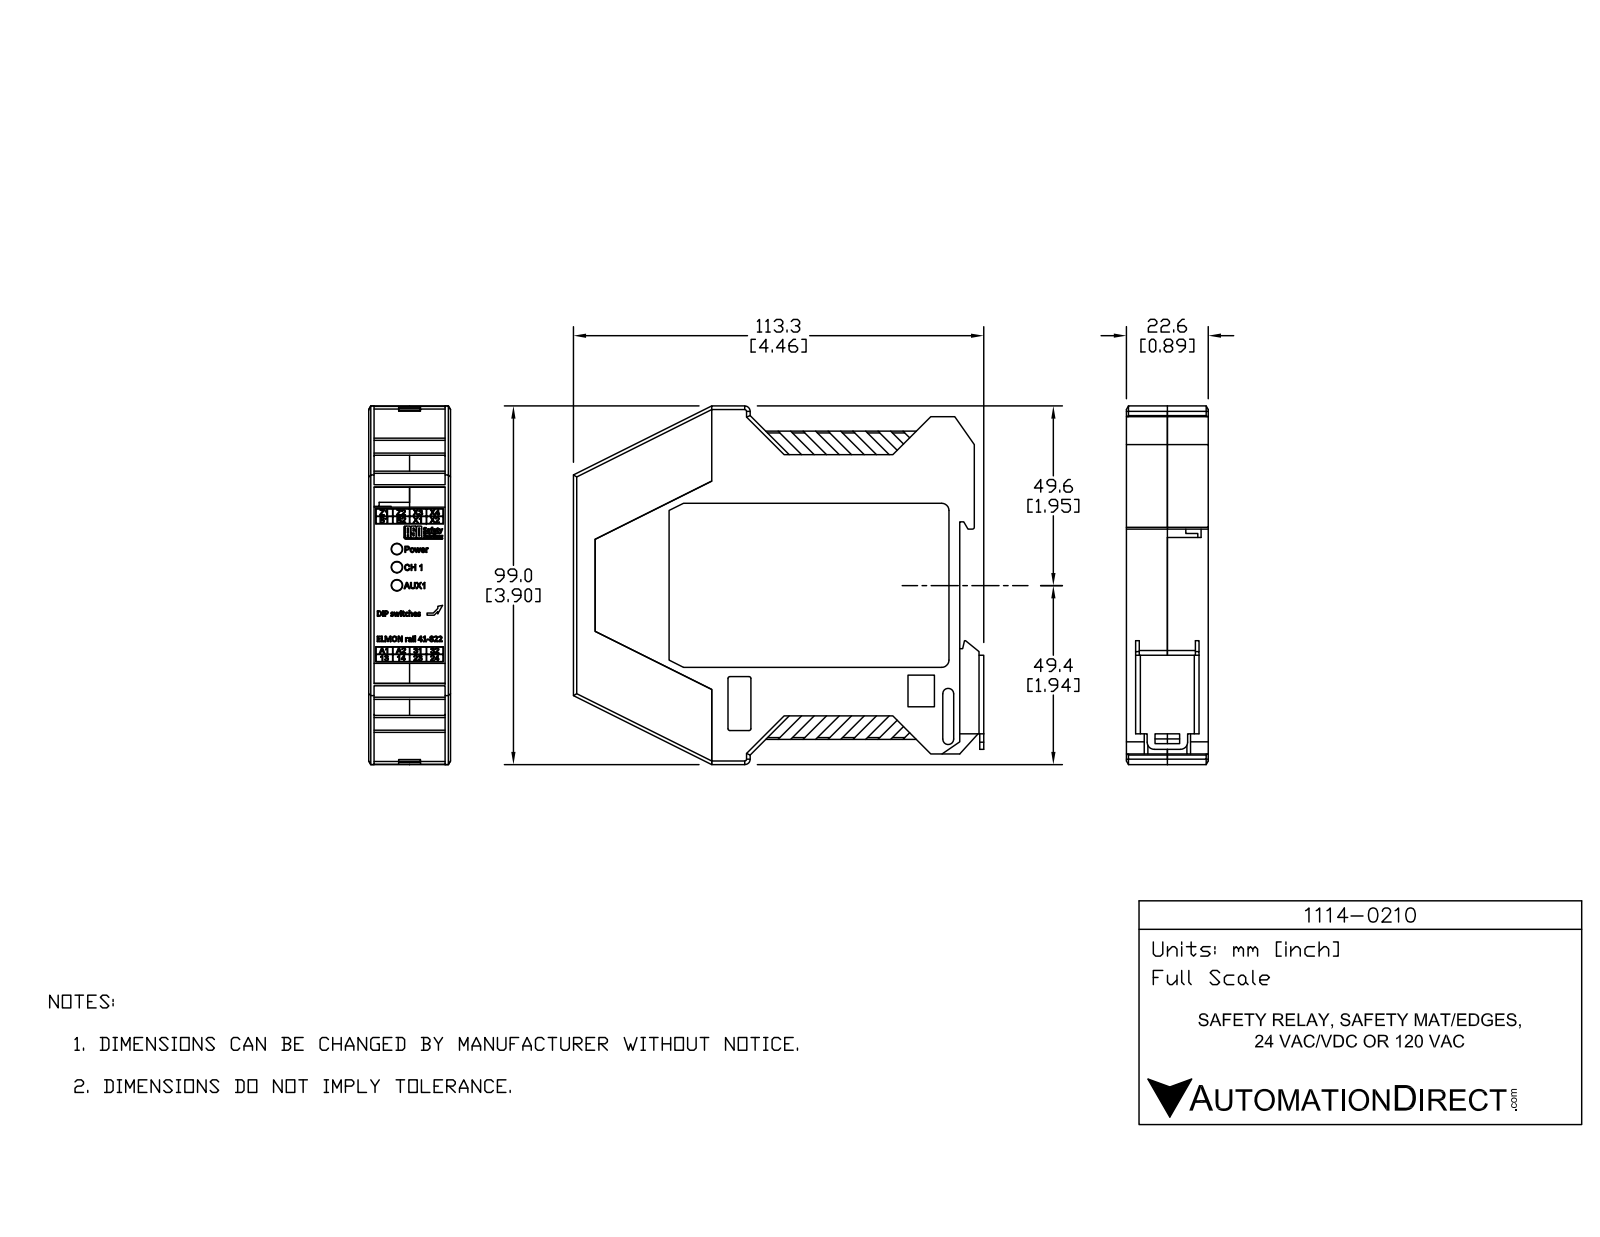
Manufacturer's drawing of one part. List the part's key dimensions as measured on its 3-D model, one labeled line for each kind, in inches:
Part name (STEP PRODUCT): 1114-0210
STEP written by: SolidWorks 2018 (AUTOMOTIVE_DESIGN)
Units: inches
Bodies: 10 solids, 2459 faces (1774 planar, 188 cylindrical, 497 other)
Overall size (bounding box): 4.461 × 3.898 × 0.89
Volume: 3.018 in³ · Surface area: 93.41 in²
Round holes (diameter × count): ⌀0.11 ×3, ⌀0.118 ×3, ⌀0.079 ×2
Round bosses / shafts (diameter × count): ⌀0.124 ×3, ⌀0.104 ×3, ⌀0.075 ×2
Partial cylindrical surfaces — rounded edges, fillets, slot ends (radius × count): R0.008 ×17, R0.015 ×10, R0.02 ×9, R0.01 ×7, R0.005 ×6, R0.01 ×5, R0.009 ×4, R0.012 ×4
Main face-to-face distances: 0.831, 0.059, 0.051, 0.882, 0.823, 0.772, 0.89, 0.445, 0.437, 0.386
Hole centre spacings: 0.197, 0.394, 3.764
